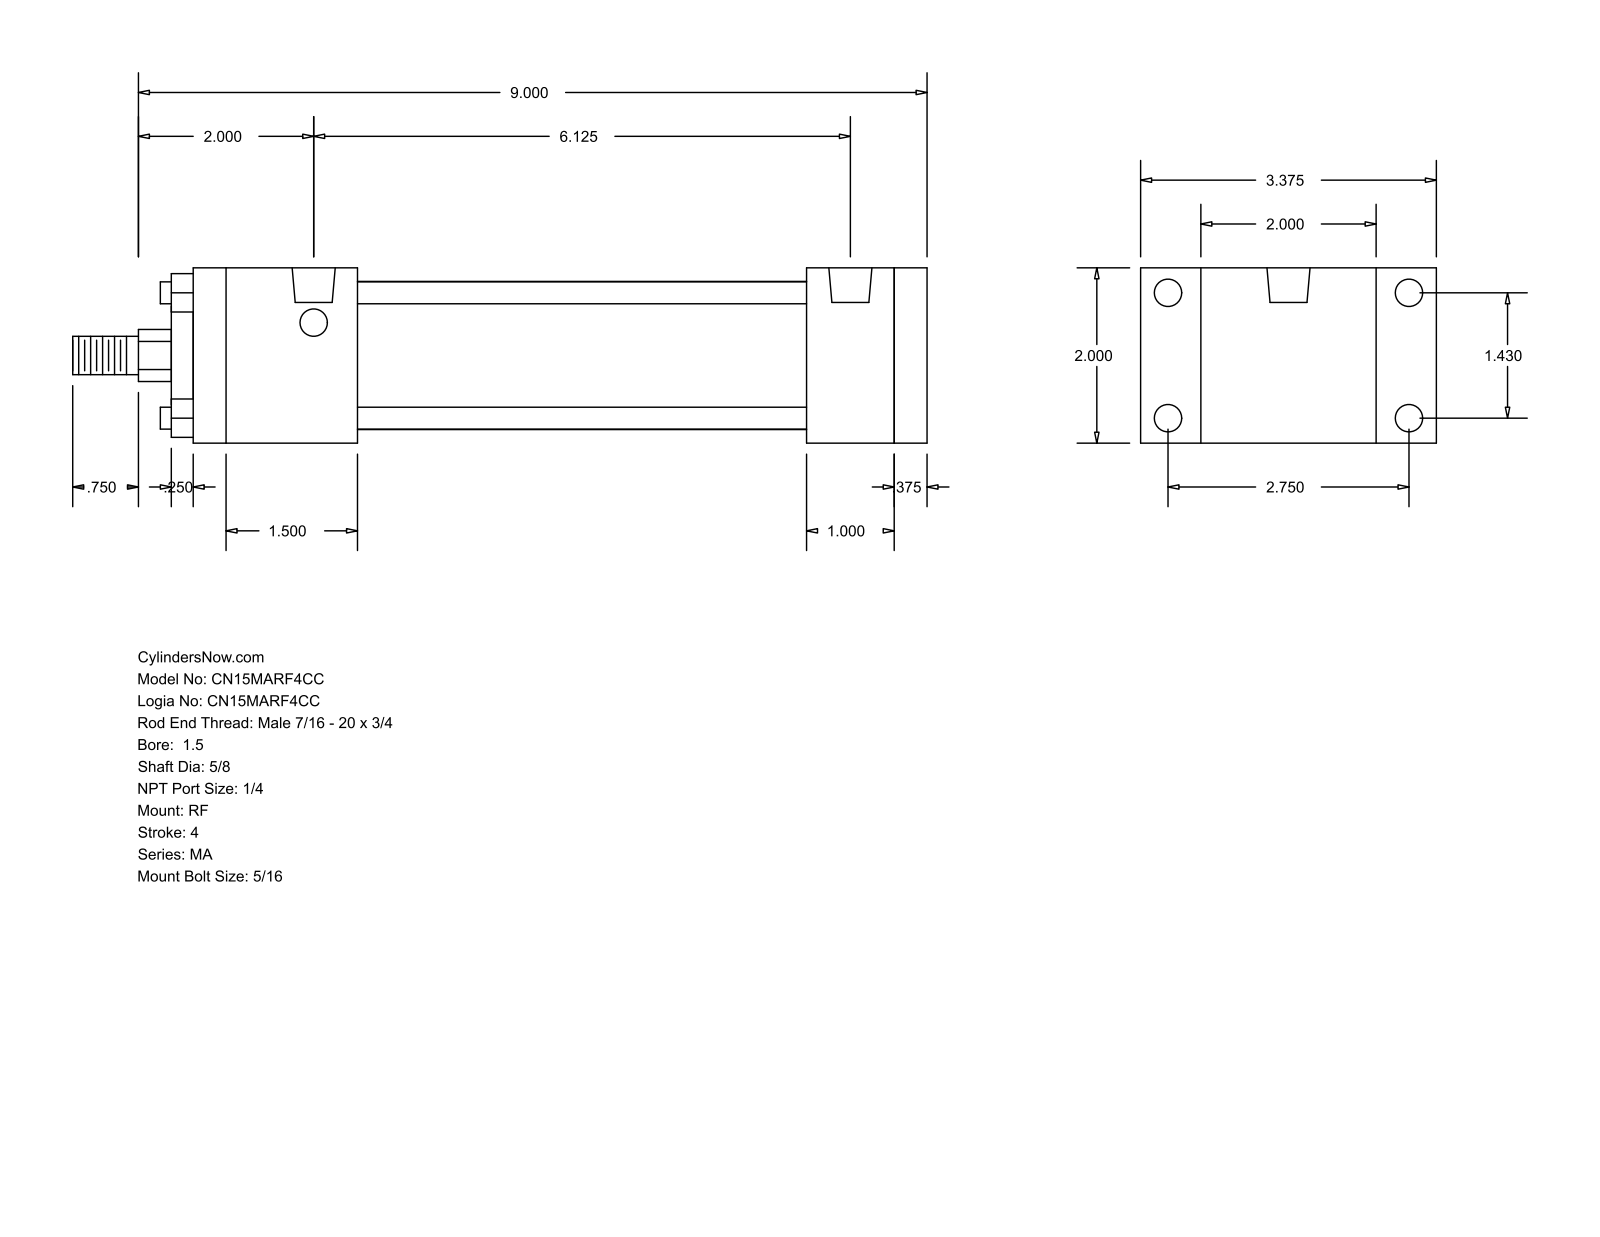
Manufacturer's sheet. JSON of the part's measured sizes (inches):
{"part_name": "MA_RF__0150_0.625", "step_written_by": "GSSL Pune (CONFIG_CONTROL_DESIGN)", "units": "inches", "bodies": {"solids": 0, "faces": 92, "planar": 64, "cylindrical": 28, "other": 0}, "overall_size": [9.75, 3.375, 2], "round_holes": [[0.313, 8], [0.492, 2]], "round_bosses_or_shafts": [[0.25, 4], [1.69, 1], [1.125, 1], [0.625, 1], [0.437, 1]], "partial_cylinders_radius": [[0.297, 1]], "face_to_face_distances": [2, 0.375, 8.375, 8, 7, 1, 1.375, 1.875, 5.125, 6.125], "hole_center_spacings": [1.43, 2.75, 3.099, 6.125]}
